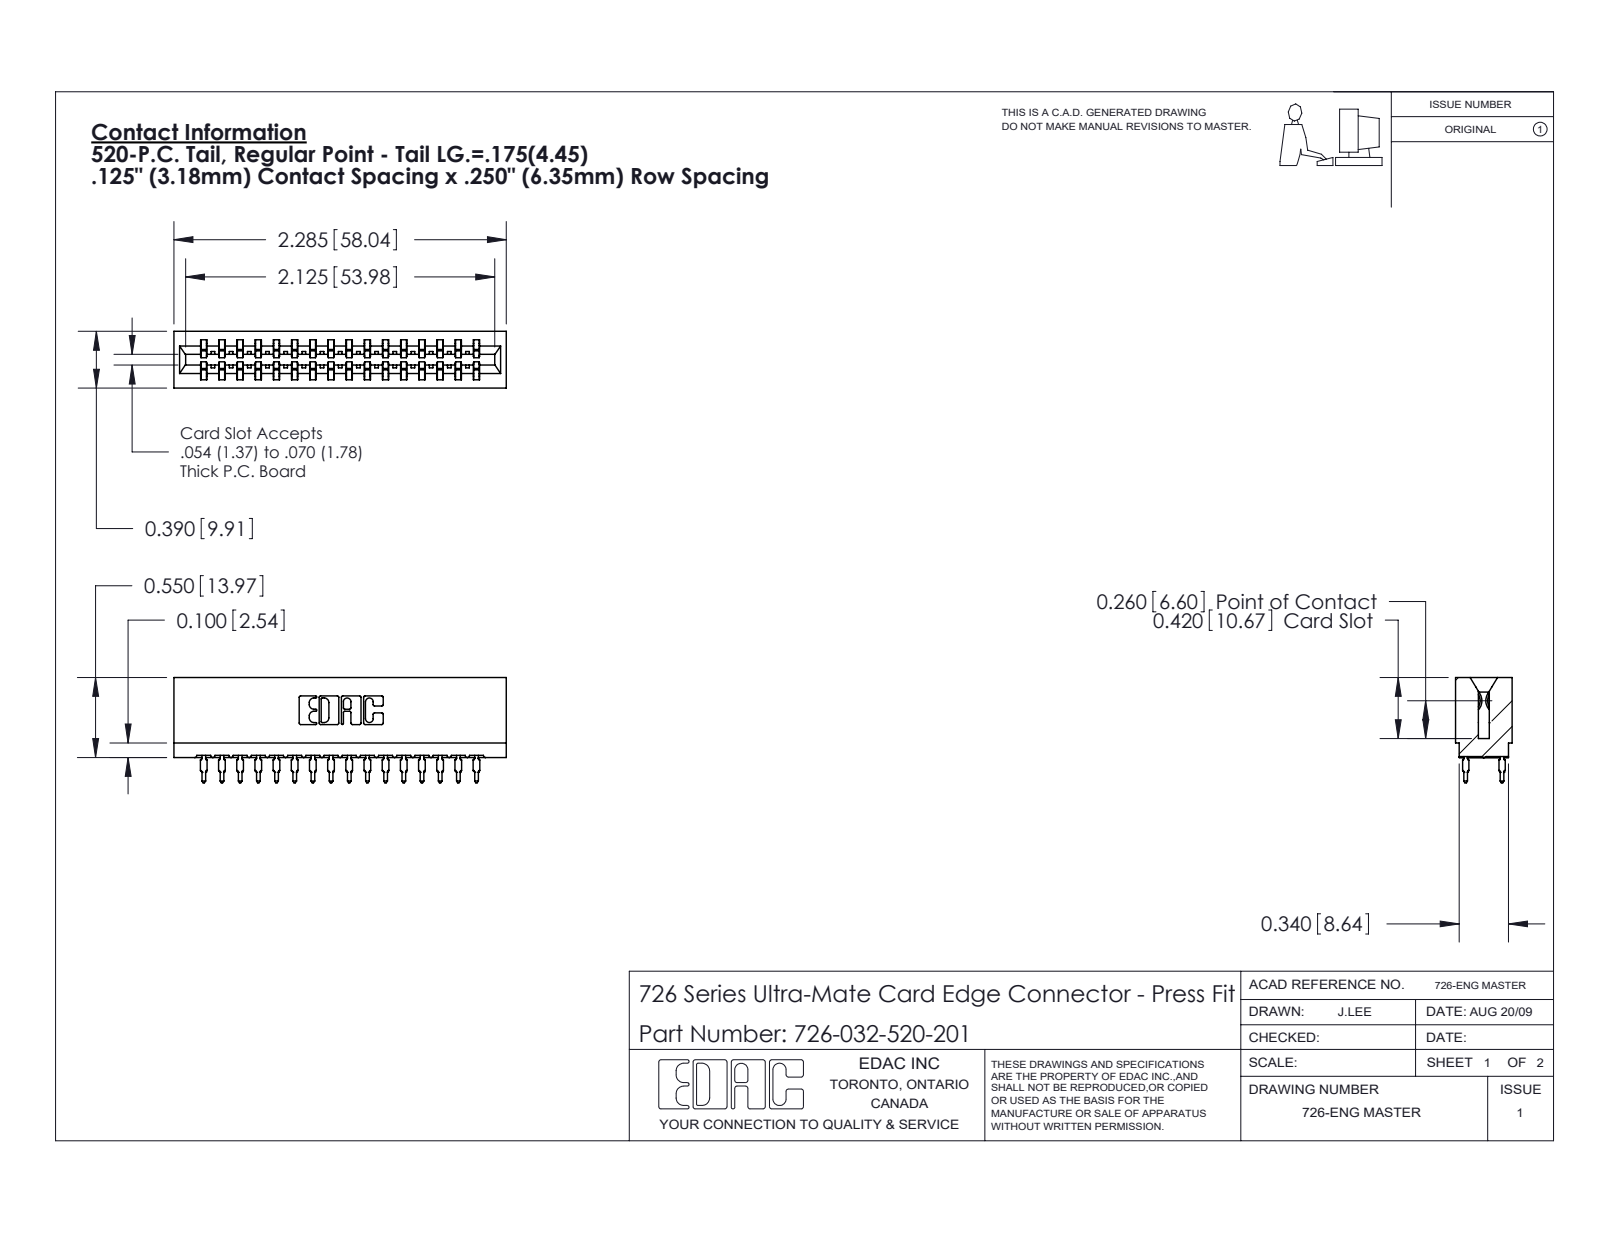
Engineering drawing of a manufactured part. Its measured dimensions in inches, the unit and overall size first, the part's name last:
Units: inches
Overall size (bounding box): 2.285 × 0.724 × 0.39
Partial cylindrical surfaces — rounded edges, fillets, slot ends (radius × count): R0.021 ×64, R0.01 ×22, R0.015 ×17, R0.005 ×8, R0.011 ×8, R0.007 ×6, R0.031 ×6, R0.026 ×3
Main face-to-face distances: 0.057, 0.333, 0.25, 0.5, 0.39, 0.025, 0.307, 0.125, 0.75, 0.083
Volume: 0.333 in³ · Surface area: 13.15 in²
Bodies: 33 solids, 2961 faces (1527 planar, 602 cylindrical, 832 other)
Part name (STEP PRODUCT): 726 Part_.515 Slot Depth - 01; 746-292-001_520; 726-032-520-201
STEP written by: SolidWorks 2020 (CONFIG_CONTROL_DESIGN)
